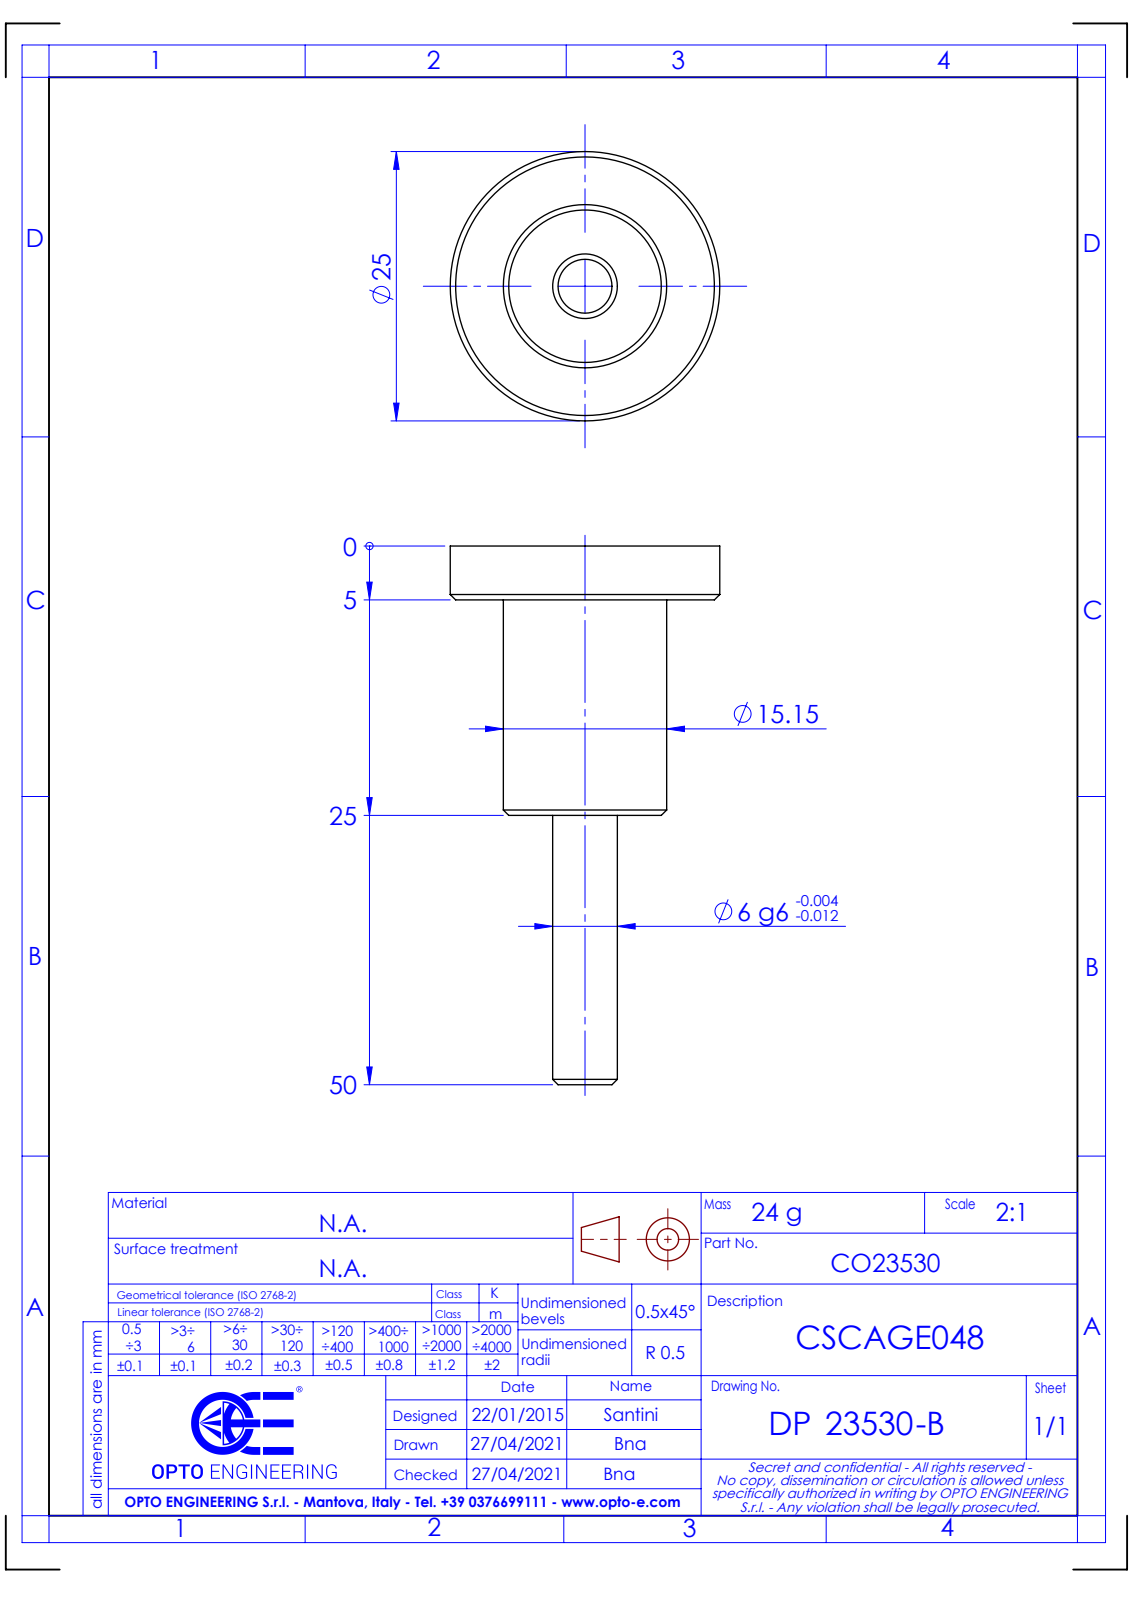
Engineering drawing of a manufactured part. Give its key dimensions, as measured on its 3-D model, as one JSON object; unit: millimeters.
{"part_name": "DP23530-B_CSCAGE048", "step_written_by": "SolidWorks 2021 (CONFIG_CONTROL_DESIGN)", "units": "millimeters", "bodies": {"solids": 0, "faces": 29, "planar": 11, "cylindrical": 8, "other": 10}, "overall_size": [50, 25, 25], "round_holes": [[5.7, 1]], "round_bosses_or_shafts": [[25, 1], [15.15, 1], [6, 1]], "face_to_face_distances": [5, 25, 20, 45, 50, 2.56]}
